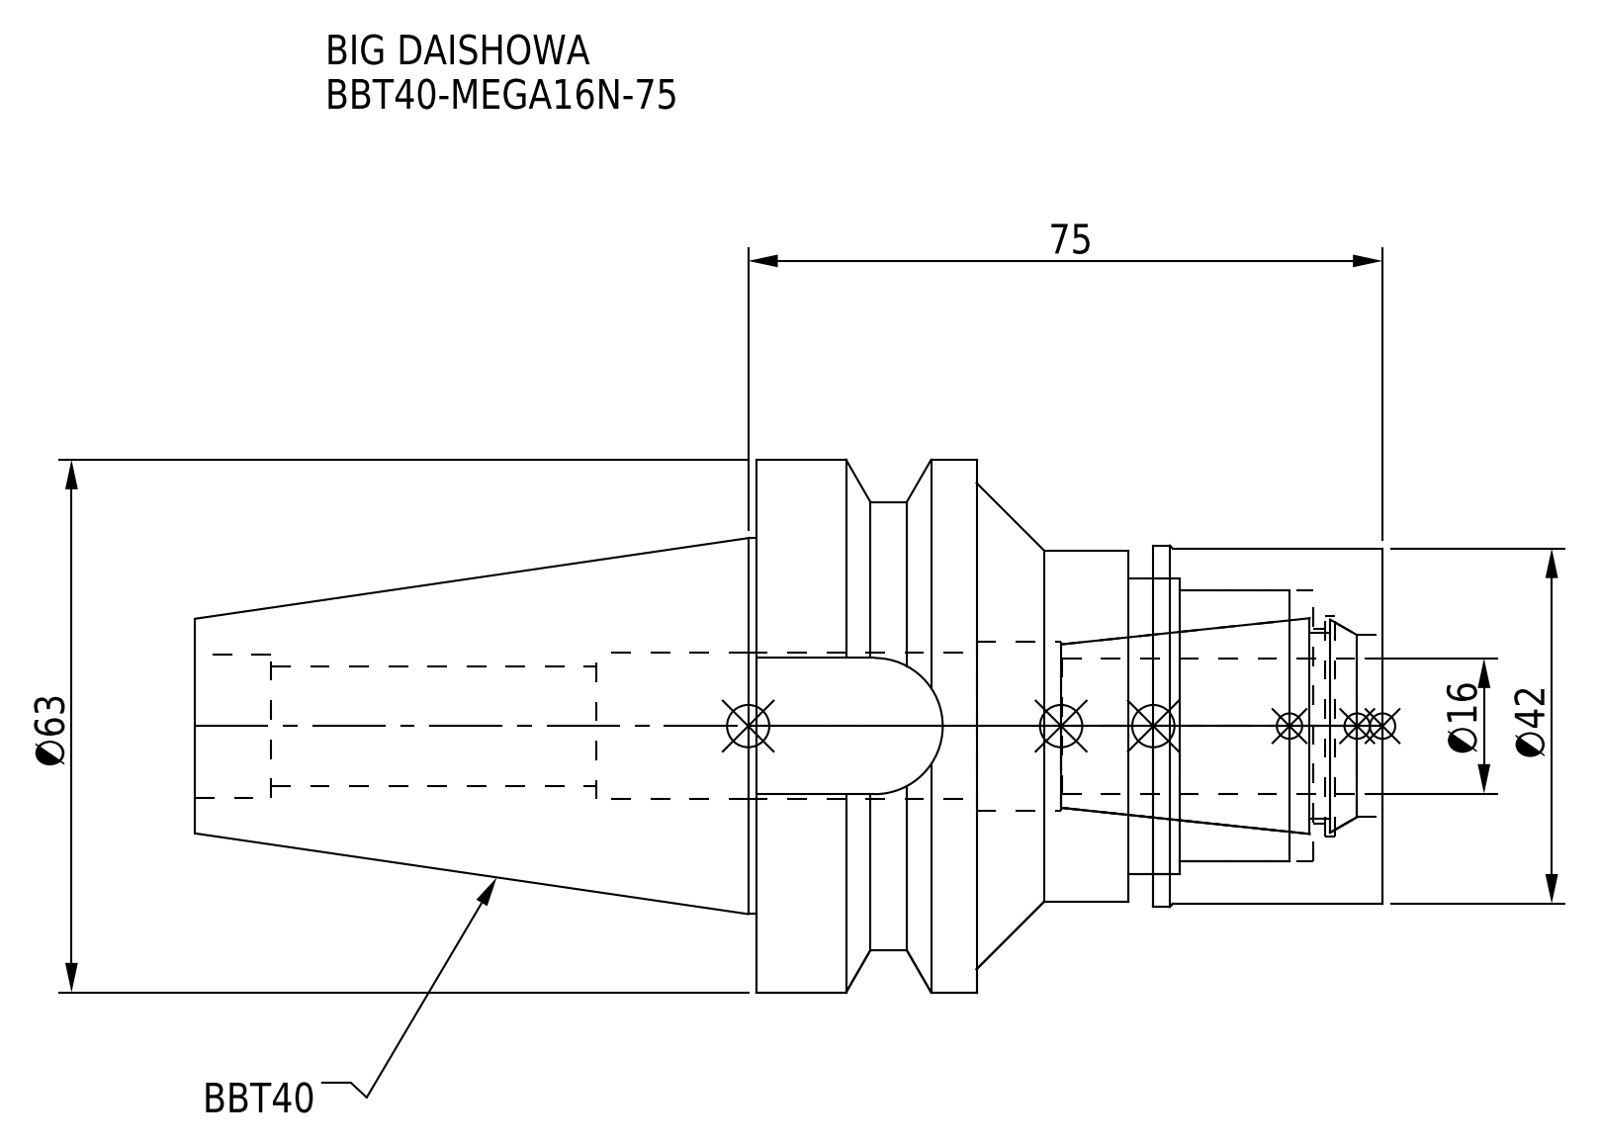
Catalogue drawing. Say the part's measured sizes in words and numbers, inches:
The part is named "BBT40MN16075-160_ASM.stp; BBT40-MEGA16N-75_1.stp; MGN16_1.stp; BBT40-MEGA16N-75 (+3 more)". Its 3-D file was written by "SolidWorks 2019 (CONFIG_CONTROL_DESIGN)". It is 2 solids with 76 faces: 22 planar, 40 cylindrical and 14 other. Overall it measures 5.528 by 2.48 by 2.48 inches. Its volume is 10.2 cubic inches and its surface area 58.35 square inches. Round holes: 1 of diameter 0.559, 1 of diameter 0.669, 1 of diameter 0.681, 1 of diameter 0.681, 1 of diameter 0.787, 1 of diameter 0.846, 1 of diameter 0.906, 1 of diameter 1.024, 1 of diameter 1.26, 1 of diameter 1.378. Round bosses or shafts: 1 of diameter 2.48, 1 of diameter 2.087, 1 of diameter 1.75, 1 of diameter 1.681, 1 of diameter 1.654, 1 of diameter 1.634. Partial cylindrical surfaces (rounded edges, fillets, slot ends): 1 of radius 0.317. The main face-to-face distances are 2.913, 0.945, 1.89, 1.024, 0.634, 1.067, 0.823, 1.846, 1.772, 1.185.
